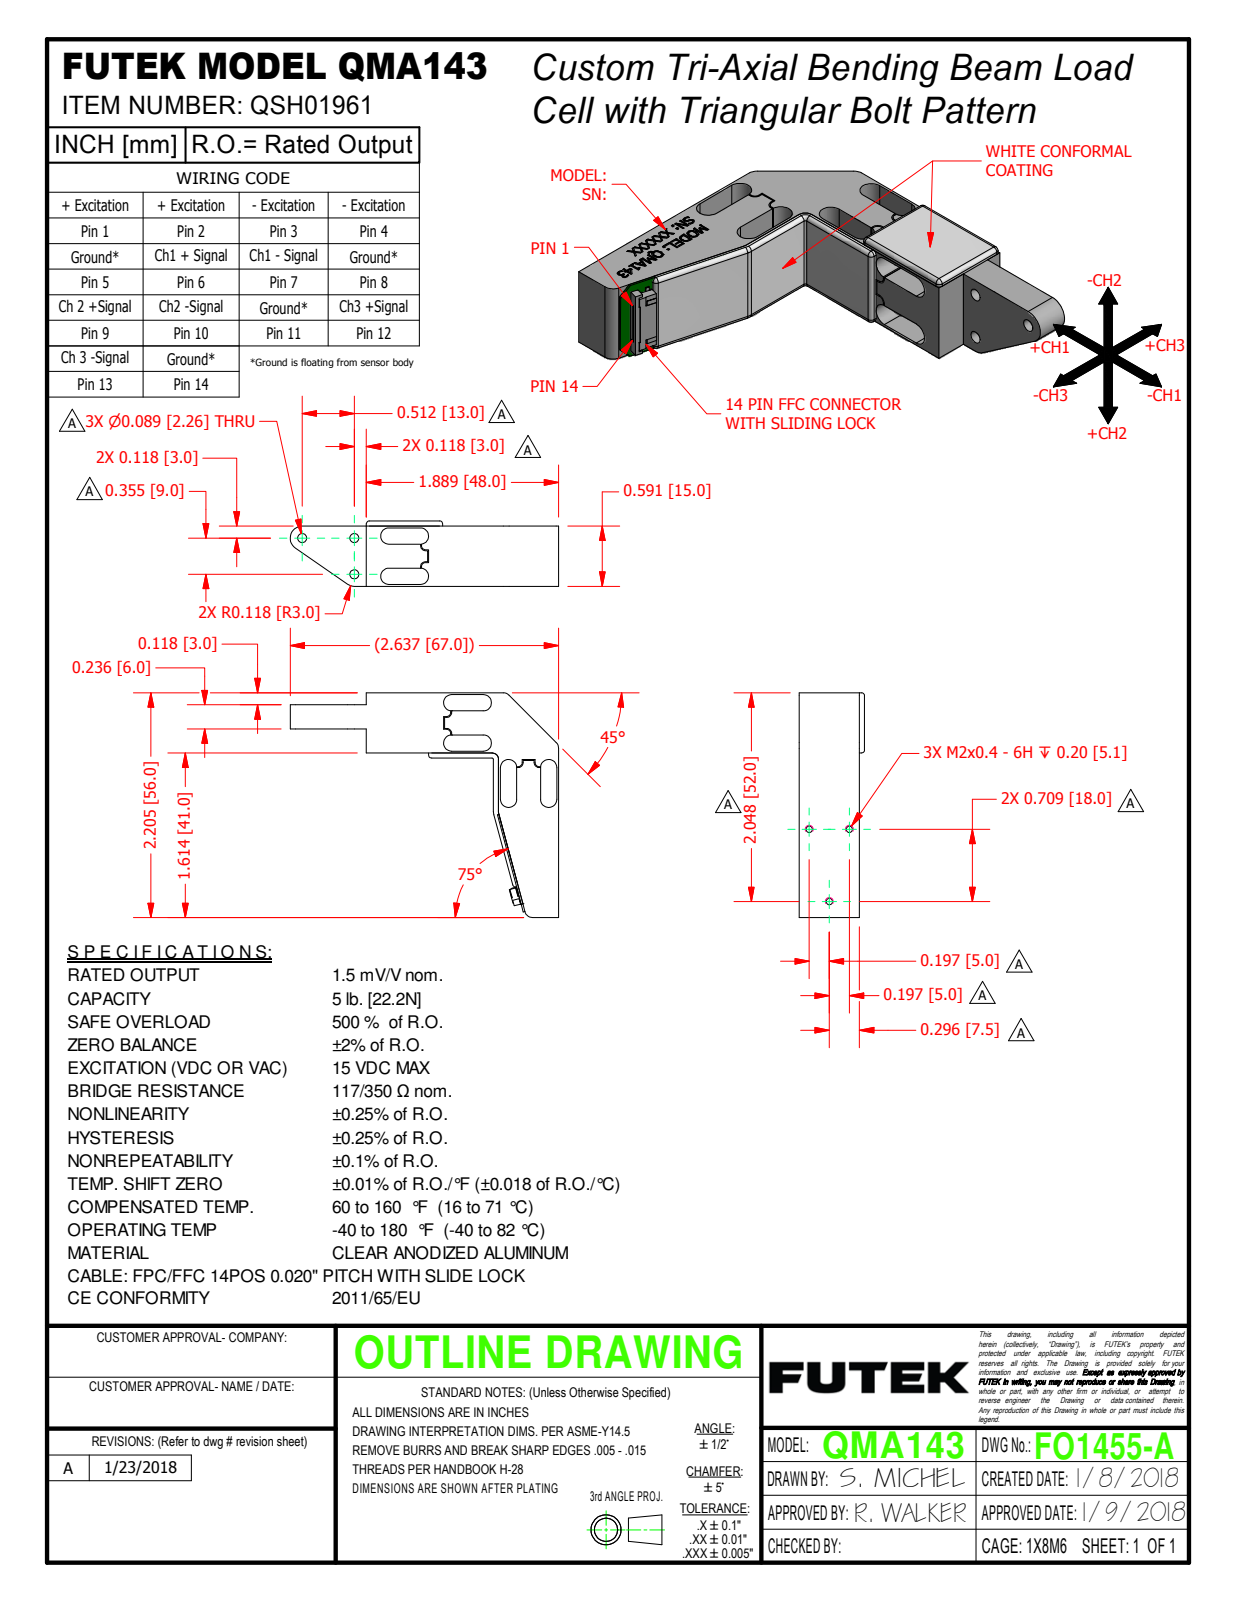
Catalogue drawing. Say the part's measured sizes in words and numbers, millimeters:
The part is named "QSH01961". Its 3-D file was written by "Autodesk Inventor 2018 (AUTOMOTIVE_DESIGN)". It is 1 solid with 488 faces: 367 planar, 106 cylindrical and 15 other. Overall it measures 67 by 56 by 16.3 millimeters. Its volume is 15 800 cubic millimeters and its surface area 9 168 square millimeters. Round holes: 3 of diameter 1.6, 3 of diameter 2.3. Partial cylindrical surfaces (rounded edges, fillets, slot ends): 20 of radius 0.8, 12 of radius 2, 6 of radius 1, 6 of radius 1.2, 3 of radius 2, 2 of radius 0.1, 2 of radius 3, 1 of radius 0.3. The main face-to-face distances are 15, 4.5, 4.1, 0.5, 10.5, 16.3, 1.3, 14.6, 10, 4.1. The hole center spacings are 18.7, 9, 10, 13, 15.8.
